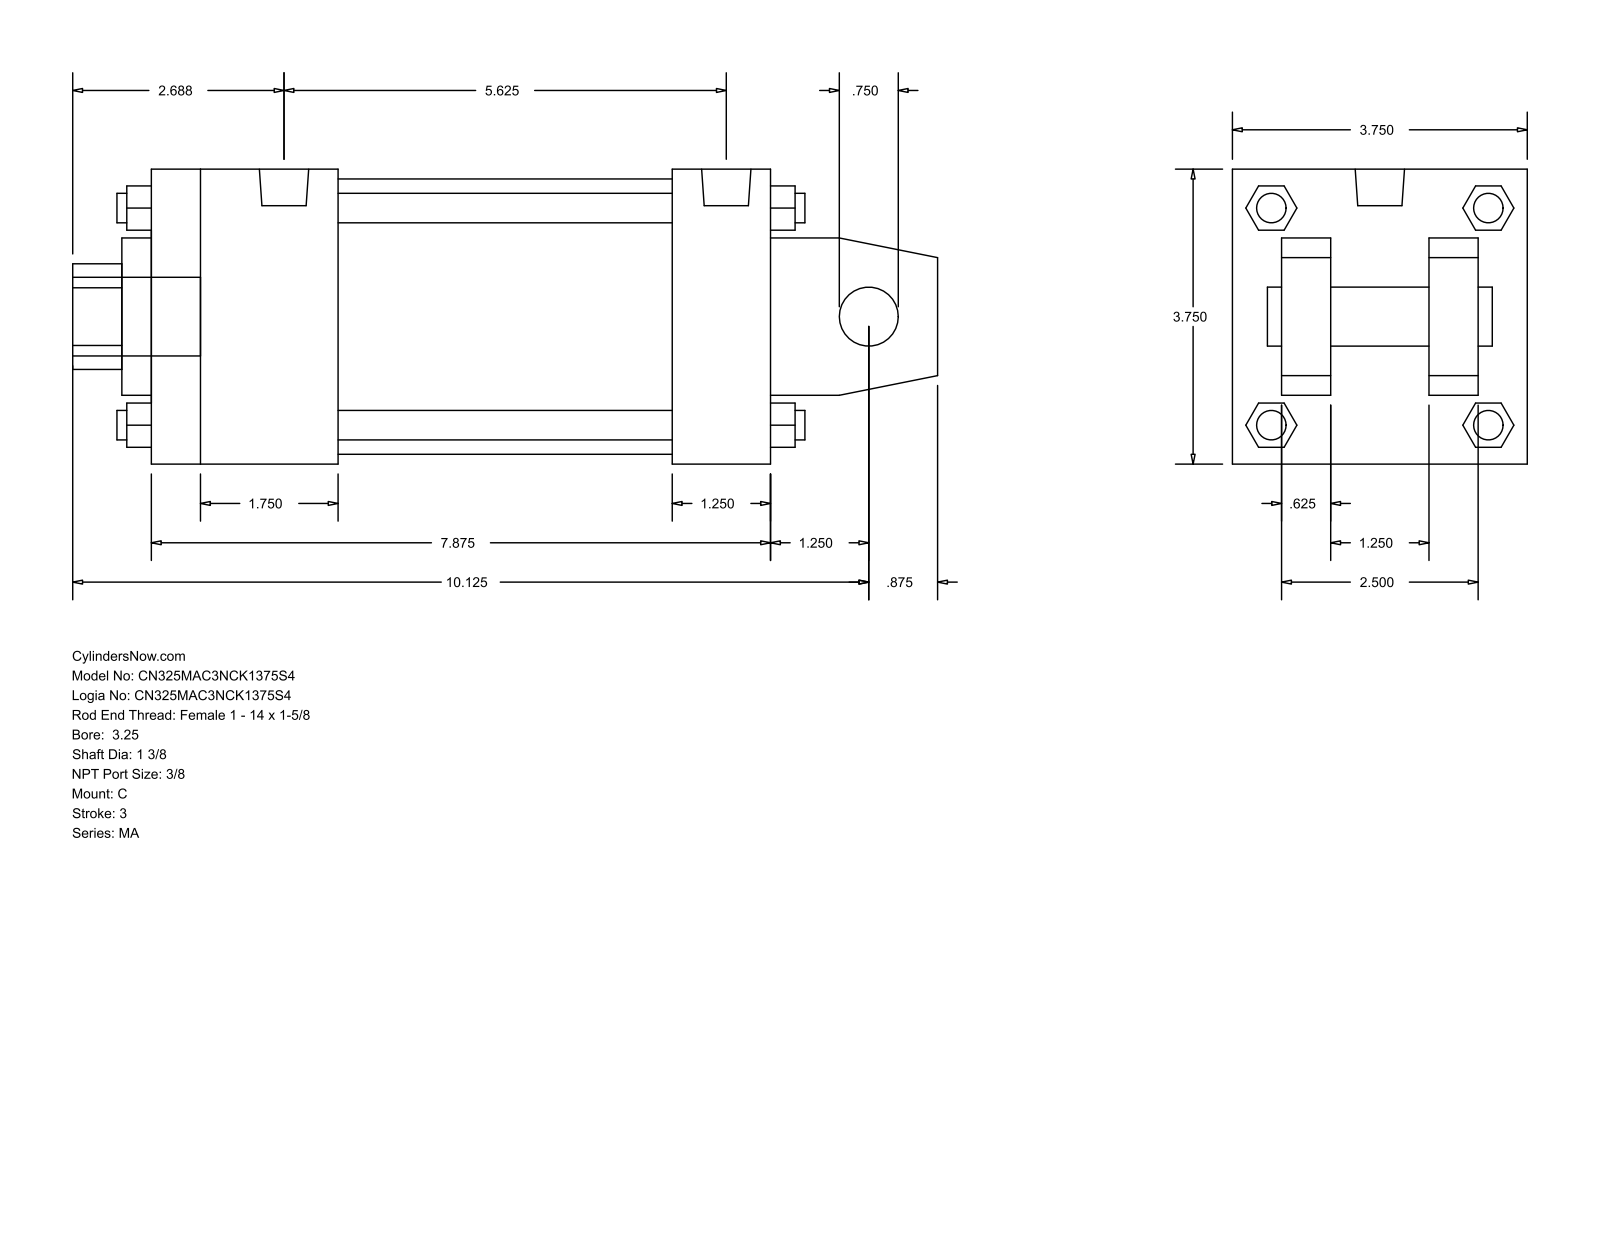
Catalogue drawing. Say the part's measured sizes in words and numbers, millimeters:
The part is named "MA_C__0325_1.375". Its 3-D file was written by "GSSL Pune (CONFIG_CONTROL_DESIGN)". It is 0 solids with 139 faces: 108 planar, 31 cylindrical and 0 other. Overall it measures 279.4 by 95.25 by 95.25 millimeters. Round holes: 1 of diameter 19.05, 1 of diameter 34.92, 1 of diameter 50.8, 1 of diameter 88.9. Round bosses or shafts: 4 of diameter 11.11, 4 of diameter 9.53, 2 of diameter 15.93, 1 of diameter 25.4. Partial cylindrical surfaces (rounded edges, fillets, slot ends): 1 of radius 17.06. The main face-to-face distances are 95.24, 15.87, 63.5, 200.03, 31.74, 79.37, 47.63, 168.28, 31.75, 60.32.
